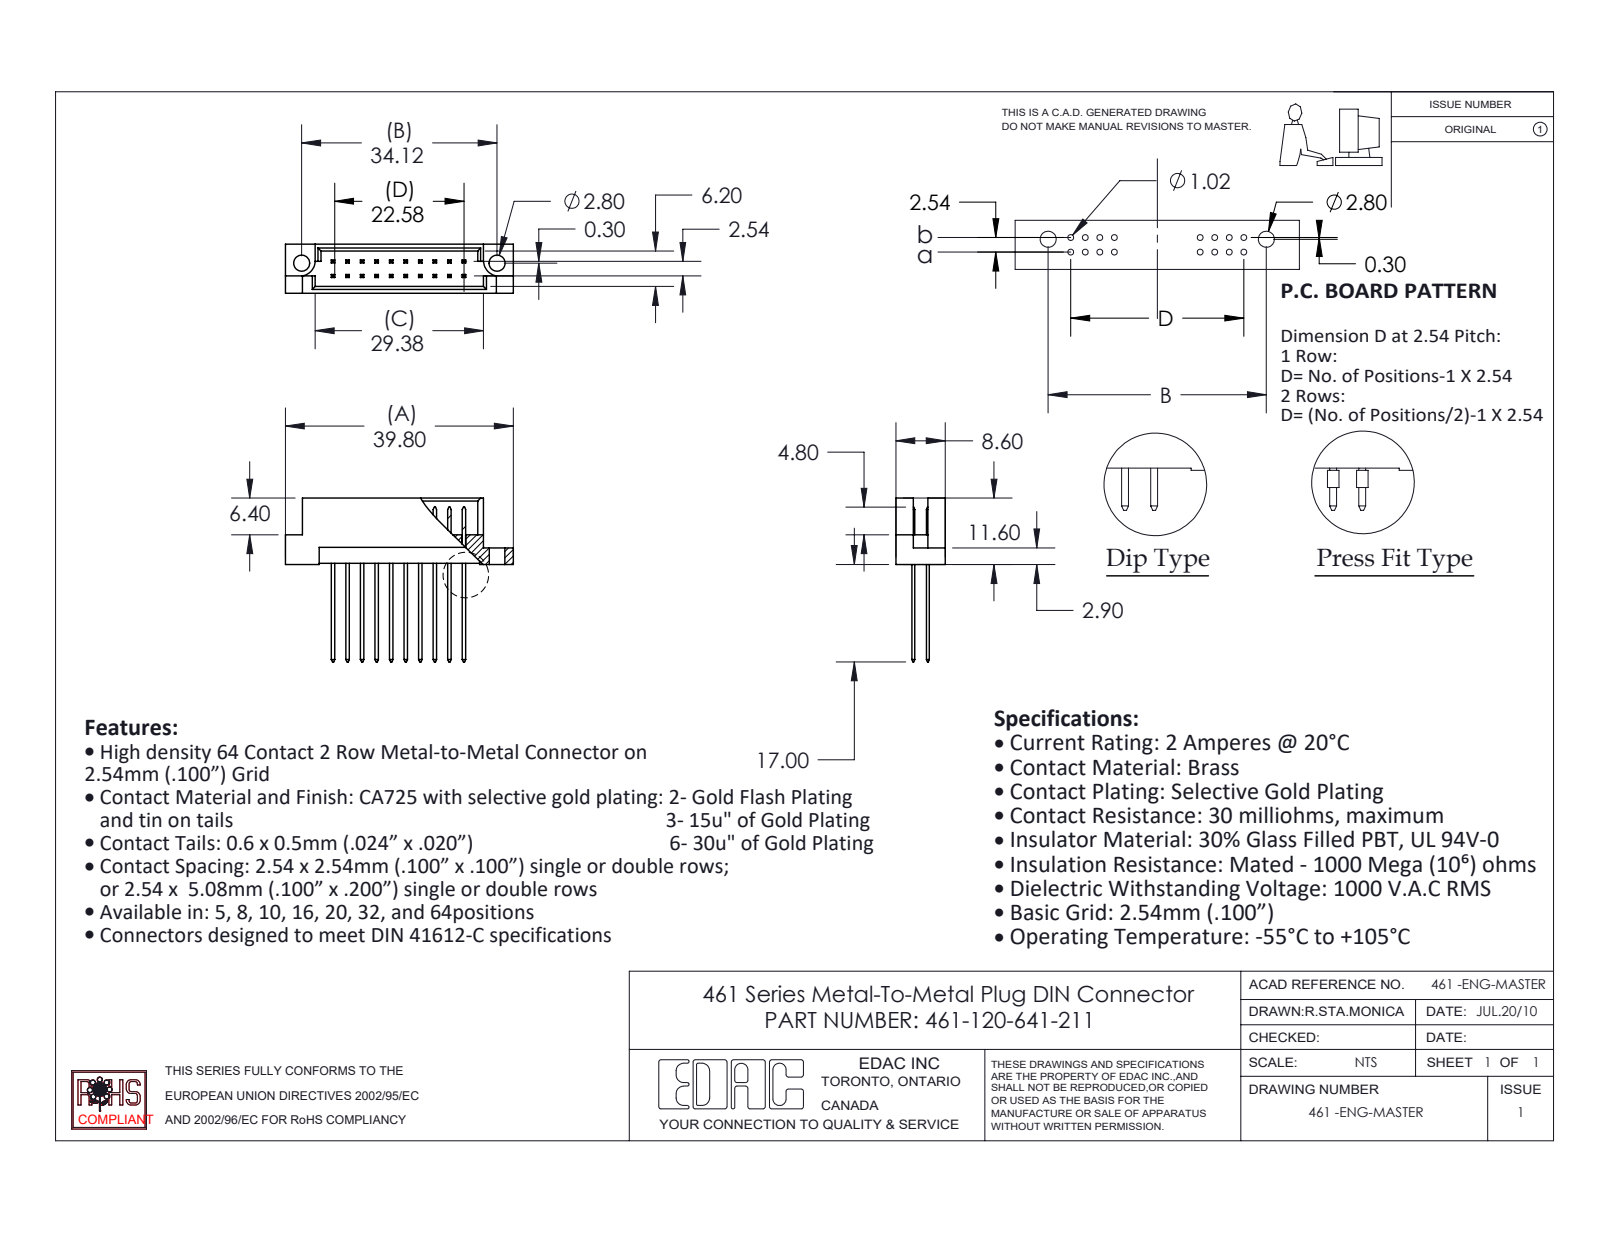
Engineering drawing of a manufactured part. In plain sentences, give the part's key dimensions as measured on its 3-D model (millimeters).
The part is named "461-120-641-211; 461 Part_20; 461-290_41". Its 3-D file was written by "SolidWorks 2020 (CONFIG_CONTROL_DESIGN)". It is 21 solids with 408 faces: 402 planar, 6 cylindrical and 0 other. Overall it measures 39.8 by 28.6 by 8.6 millimeters. Its volume is 2 064 cubic millimeters and its surface area 3 518 square millimeters. Round holes: 2 of diameter 2.8. Partial cylindrical surfaces (rounded edges, fillets, slot ends): 2 of radius 2.8. The main face-to-face distances are 2.54, 1.2, 7.4, 2.78, 3.28, 5.32, 5.82, 1.58, 2.08, 4.12. The hole center spacings are 34.12.
